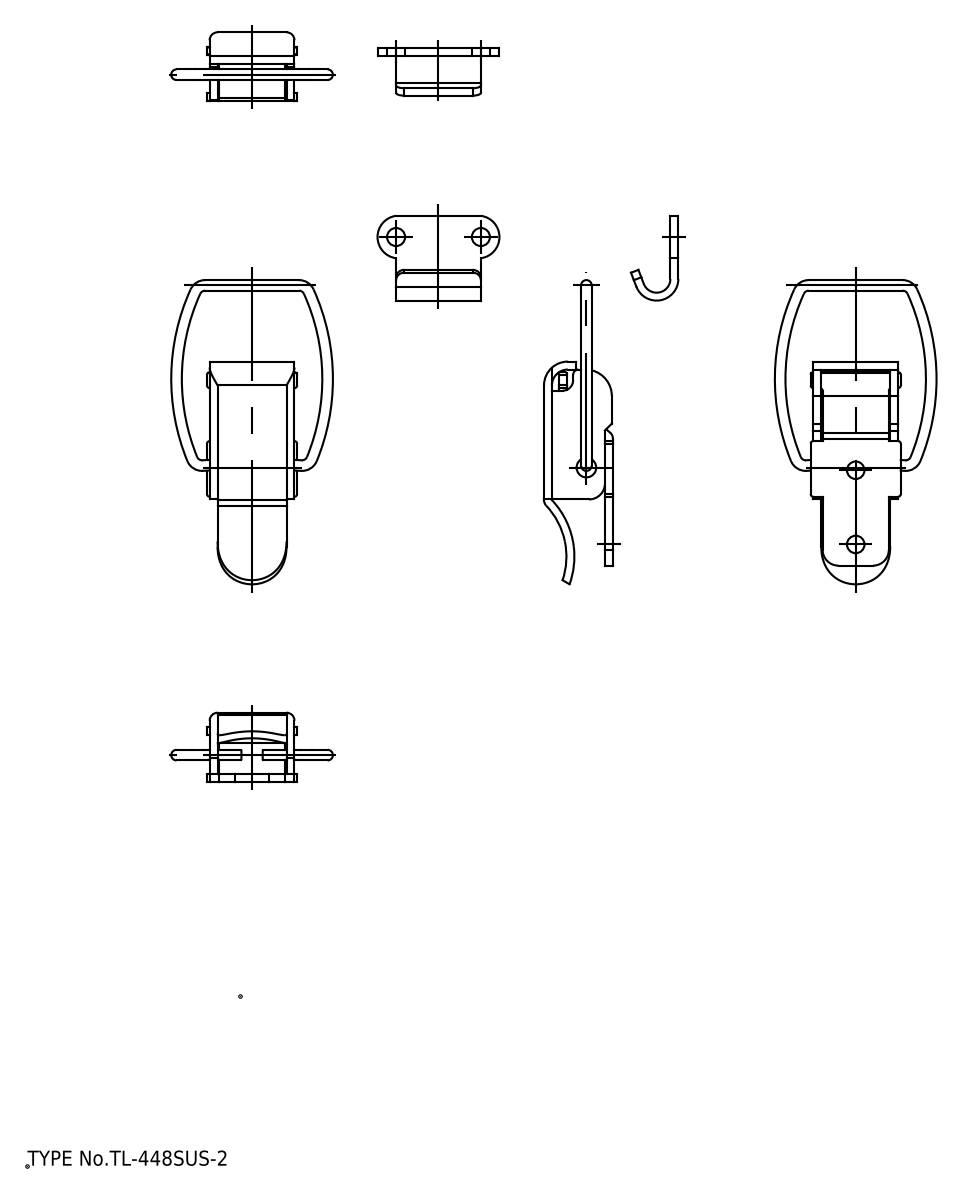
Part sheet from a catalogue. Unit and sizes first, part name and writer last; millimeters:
Units: millimetres
Overall size (bounding box): 69.52 × 30.5 × 13
Round holes (diameter × count): ⌀3.3 ×2, ⌀3.4 ×2, ⌀3.7 ×1
Round bosses / shafts (diameter × count): ⌀2 ×3
Partial cylindrical surfaces — rounded edges, fillets, slot ends (radius × count): R0.5 ×10, R1.5 ×8, R3 ×4, R0.2 ×2, R4.04 ×2, R1 ×1, R2 ×1, R2.6 ×1
Main face-to-face distances: 1.5, 11.5, 13, 14.5, 10, 16, 2.75, 8.75, 1.75, 14.25
Hole centre spacings: 44.72, 58.55, 14, 16
Volume: 3 412 mm³ · Surface area: 5 434 mm²
Bodies: 4 solids, 128 faces (59 planar, 57 cylindrical, 12 other)
Part name (STEP PRODUCT): アーム; ベース; レバー; TL-176SUS-7
STEP written by: spGate 20.6.3 (****-****-****-****) (AUTOMOTIVE_DESIGN)
